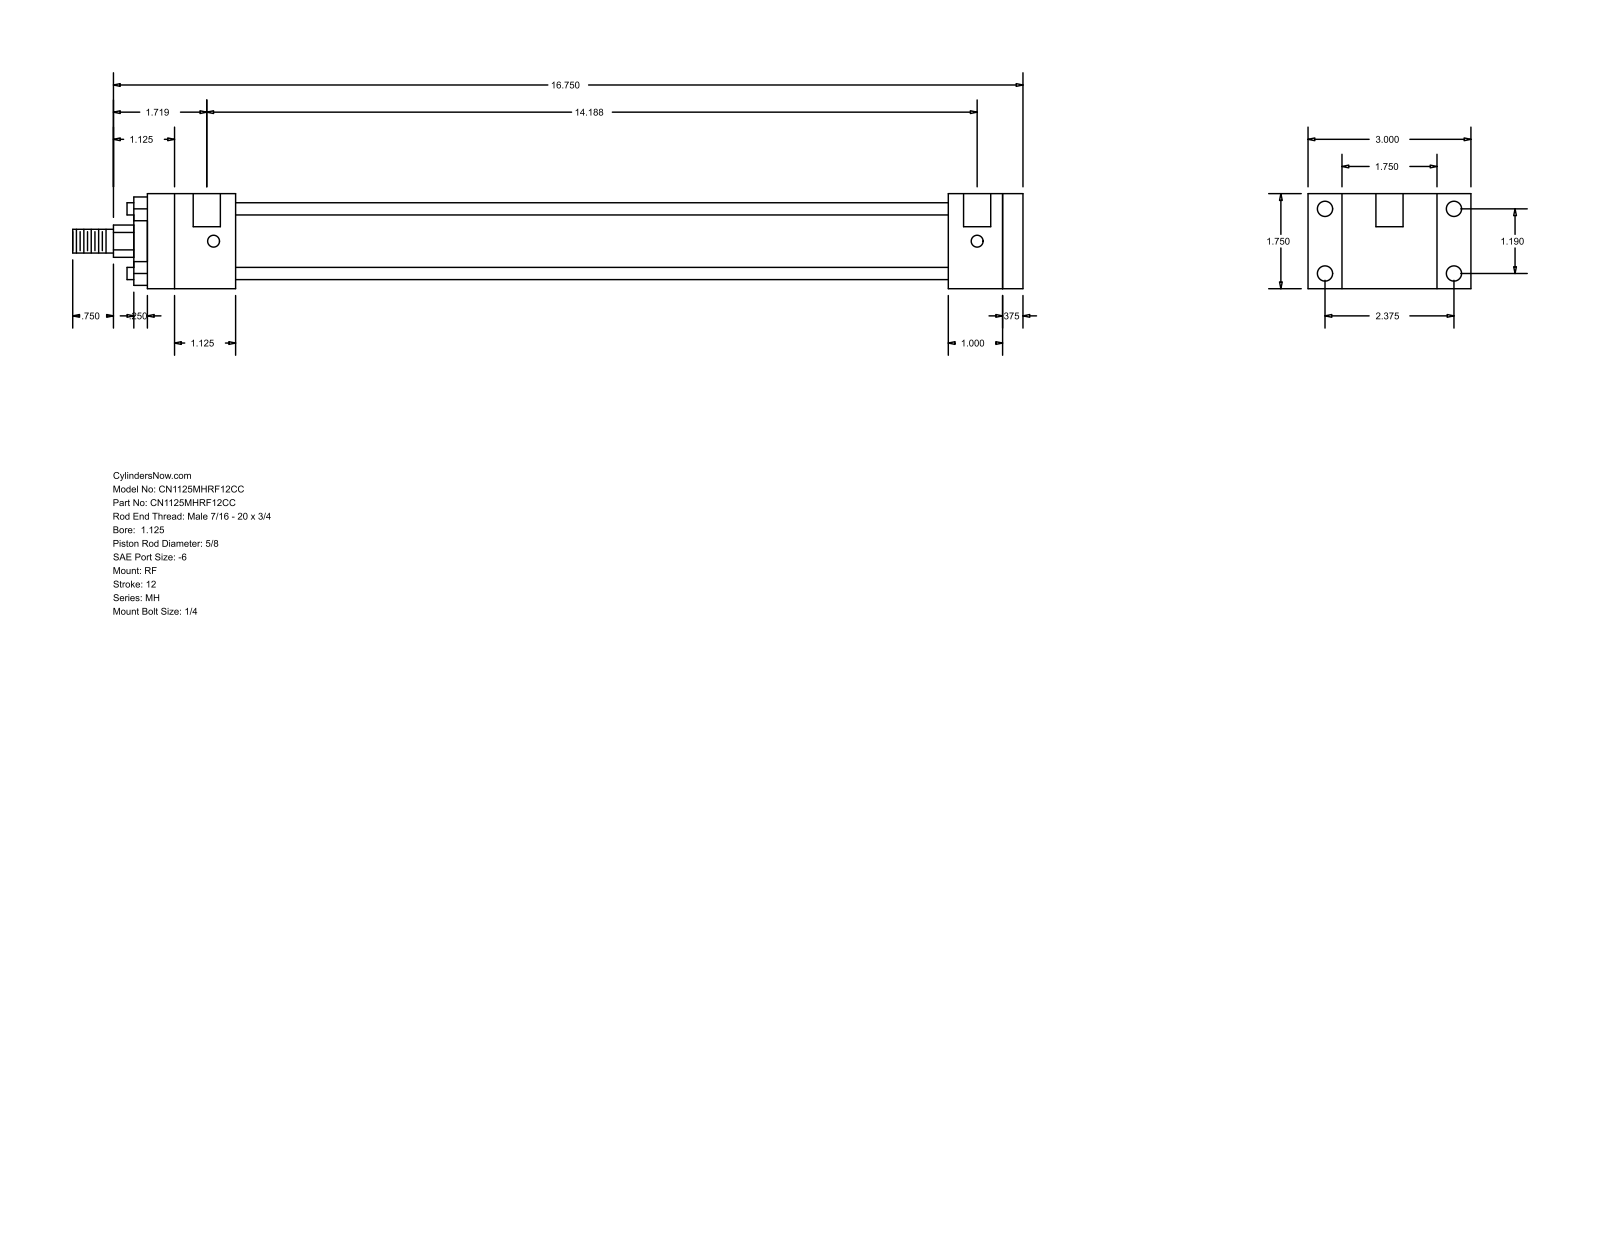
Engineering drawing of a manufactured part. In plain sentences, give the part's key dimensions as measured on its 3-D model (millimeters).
The part is named "MH_RF__0112_0.625". Its 3-D file was written by "GSSL Pune (CONFIG_CONTROL_DESIGN)". It is 0 solids with 92 faces: 64 planar, 28 cylindrical and 0 other. Overall it measures 444.5 by 76.2 by 44.45 millimeters. Round holes: 4 of diameter 5.56, 4 of diameter 7.14, 2 of diameter 12.7. Round bosses or shafts: 4 of diameter 5.71, 1 of diameter 34.92, 1 of diameter 28.57, 1 of diameter 15.88, 1 of diameter 11.11. Partial cylindrical surfaces (rounded edges, fillets, slot ends): 1 of radius 7.54. The main face-to-face distances are 44.46, 9.52, 34.93, 409.57, 15.87, 358.78, 368.3, 333.37, 25.41, 41.27. The hole center spacings are 30.22, 60.32, 67.47, 357.19, 3.17, 360.36.
